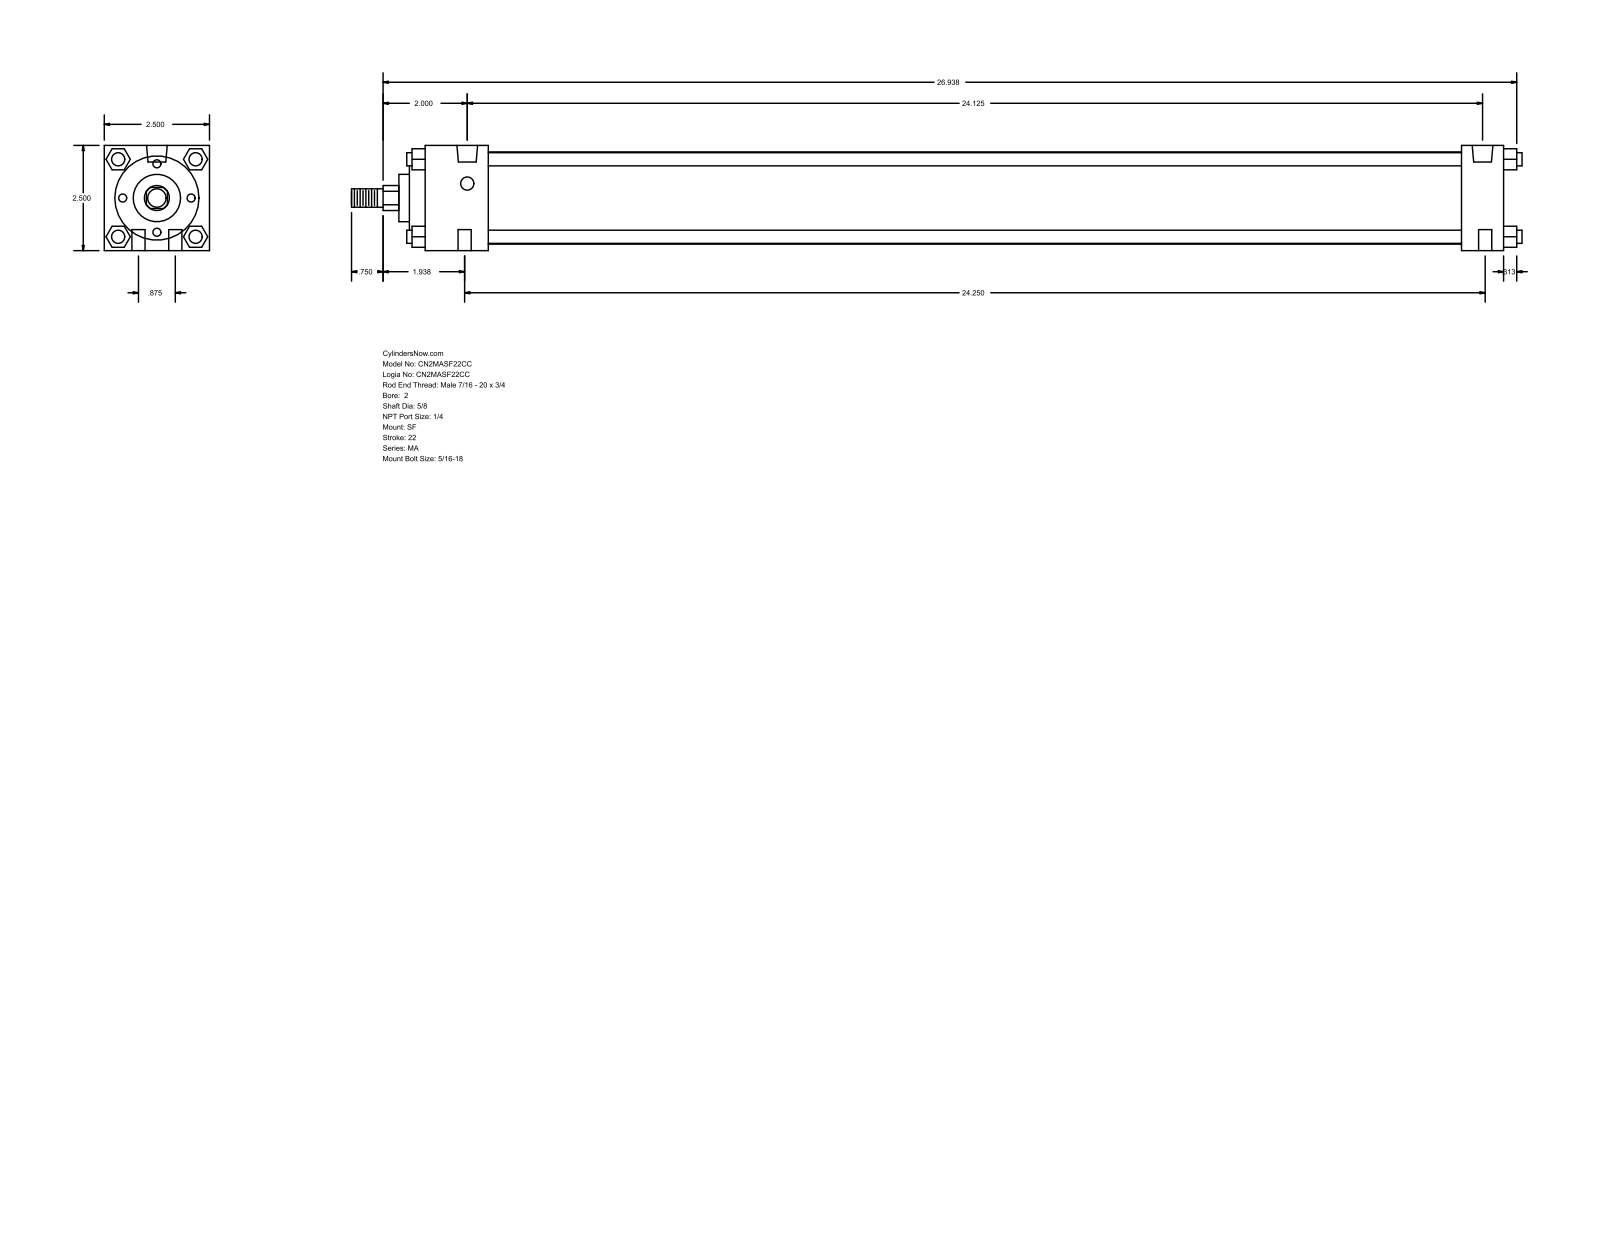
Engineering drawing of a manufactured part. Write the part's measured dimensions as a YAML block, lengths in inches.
part_name: "MA_SF__0200_0.625"
step_written_by: "GSSL Pune (CONFIG_CONTROL_DESIGN)"
units: inches
bodies: {solids: 0, faces: 126, planar: 95, cylindrical: 31, other: 0}
overall_size: [27.813, 2.5, 2.5]
round_holes:
  - {diameter: 0.313, count: 6}
  - {diameter: 0.492, count: 2}
round_bosses_or_shafts:
  - {diameter: 0.313, count: 4}
  - {diameter: 2.19, count: 1}
  - {diameter: 2, count: 1}
  - {diameter: 1.125, count: 1}
  - {diameter: 0.625, count: 1}
  - {diameter: 0.437, count: 1}
partial_cylinders:
  - {radius: 0.297, count: 1}
face_to_face_distances: [2.5, 0.5, 1.5, 25.625, 24.625, 1, 23.125, 24.125, 0.375, 1.875]
hole_center_spacings: [0.442, 0.875, 24.125, 24.191, 24.192, 24.25, 24.266]
